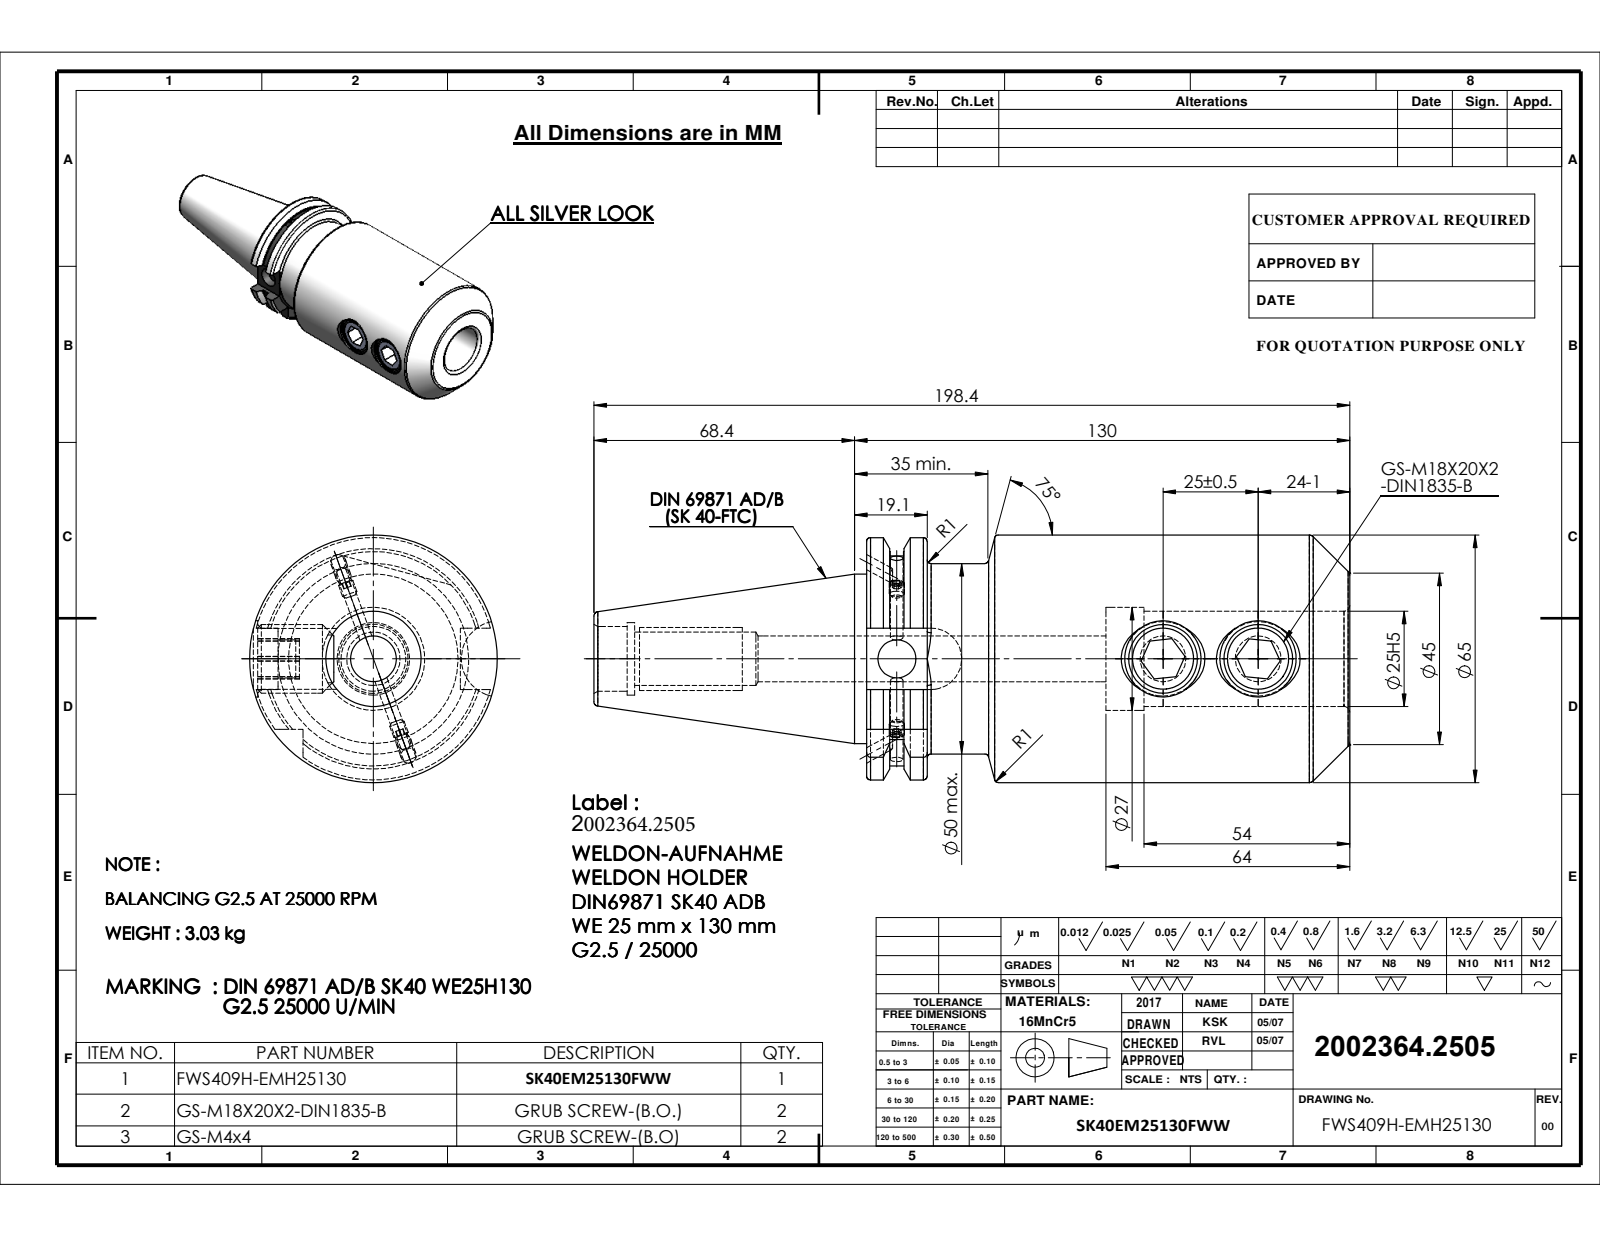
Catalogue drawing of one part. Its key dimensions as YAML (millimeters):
part_name: "SK40EM25130FWW; Copy of M4X4_DIN 913 - M4 x 4-N; GS-M18X2X20; 91406-WE725130"
step_written_by: "SolidWorks 2009 (CONFIG_CONTROL_DESIGN)"
units: millimeters
bodies: {solids: 5, faces: 197, planar: 69, cylindrical: 53, other: 75}
overall_size: [198.4, 65, 65]
volume: 393882
surface_area: 56389
round_holes:
  - {diameter: 16, count: 2}
  - {diameter: 20, count: 2}
  - {diameter: 3.3, count: 1}
  - {diameter: 10, count: 1}
  - {diameter: 12, count: 1}
  - {diameter: 14, count: 1}
  - {diameter: 17, count: 1}
  - {diameter: 19, count: 1}
  - {diameter: 25, count: 1}
  - {diameter: 27, count: 1}
round_bosses_or_shafts:
  - {diameter: 18, count: 2}
  - {diameter: 4, count: 2}
  - {diameter: 65, count: 1}
  - {diameter: 50, count: 1}
  - {diameter: 44.45, count: 1}
partial_cylinders:
  - {radius: 8.05, count: 1}
  - {radius: 28.12, count: 1}
  - {radius: 31.77, count: 1}
face_to_face_distances: [126.8, 15.9, 110.9, 10, 62.8, 46.9, 64, 53.2, 20, 33.2]
hole_center_spacings: [25, 69.85, 94.85]
